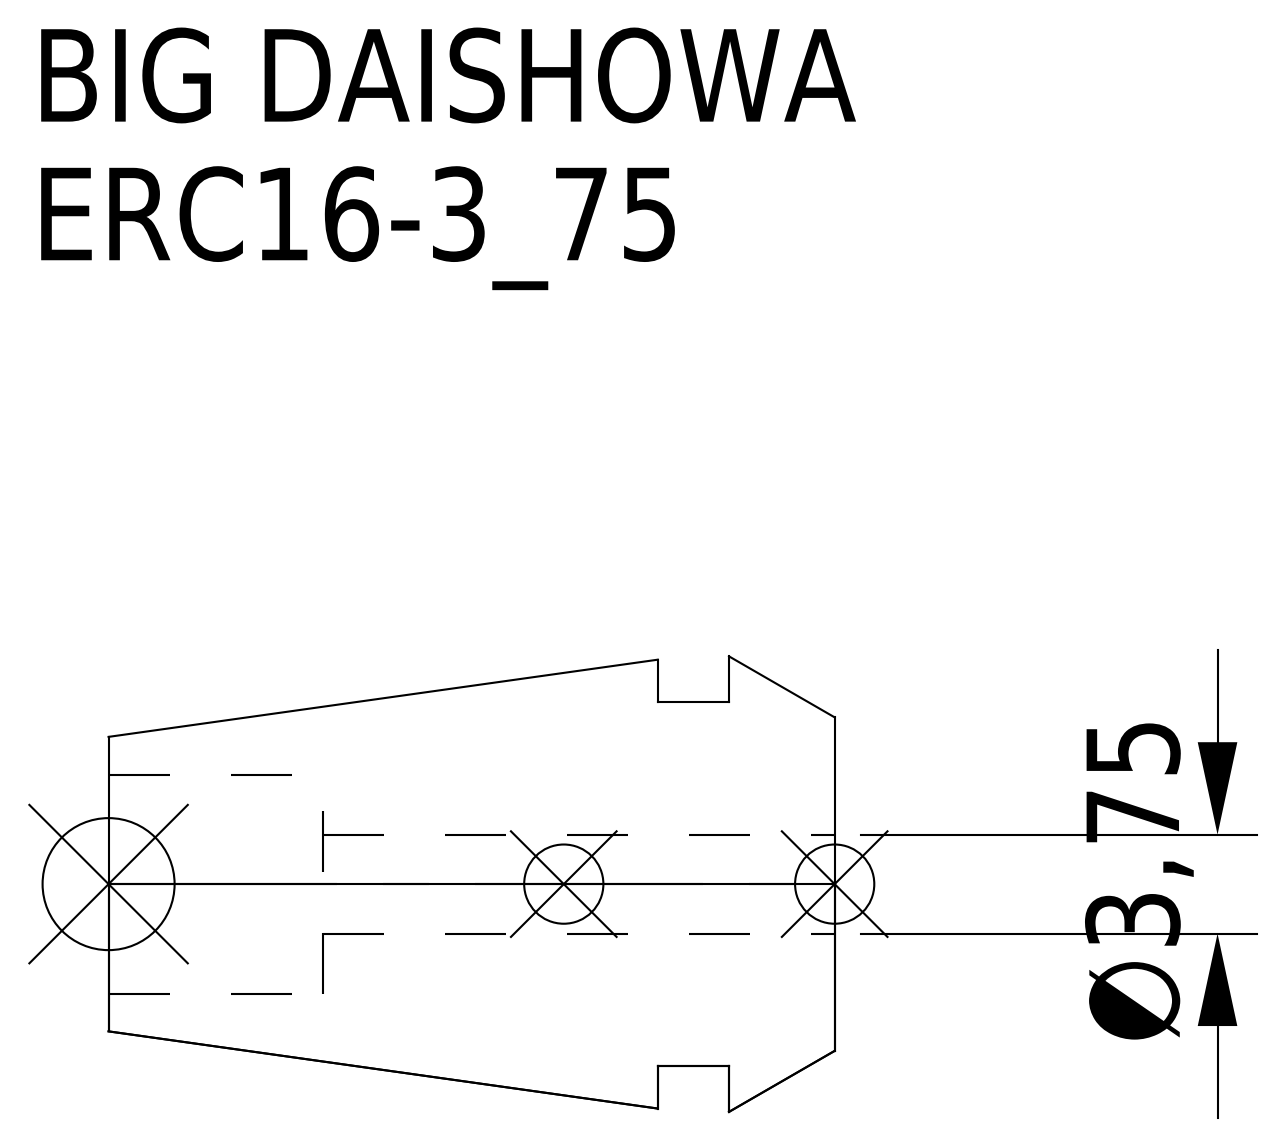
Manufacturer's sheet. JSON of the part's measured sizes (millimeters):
{"part_name": "ERC16-3_75", "step_written_by": "CREO PARAMETRIC BY PTC INC, 2016380 (AUTOMOTIVE_DESIGN)", "units": "millimeters", "bodies": {"solids": 1, "faces": 15, "planar": 5, "cylindrical": 6, "other": 4}, "overall_size": [27.5, 17.25, 17.25], "volume_mm3": 3741, "surface_area_mm2": 2065, "round_holes": [[3.75, 1], [8.3, 1]], "round_bosses_or_shafts": [[13.8, 1]], "face_to_face_distances": [4, 6.7, 2.7, 27.5, 23.5, 20.8, 19.37, 15.37, 12.67, 8.13]}
